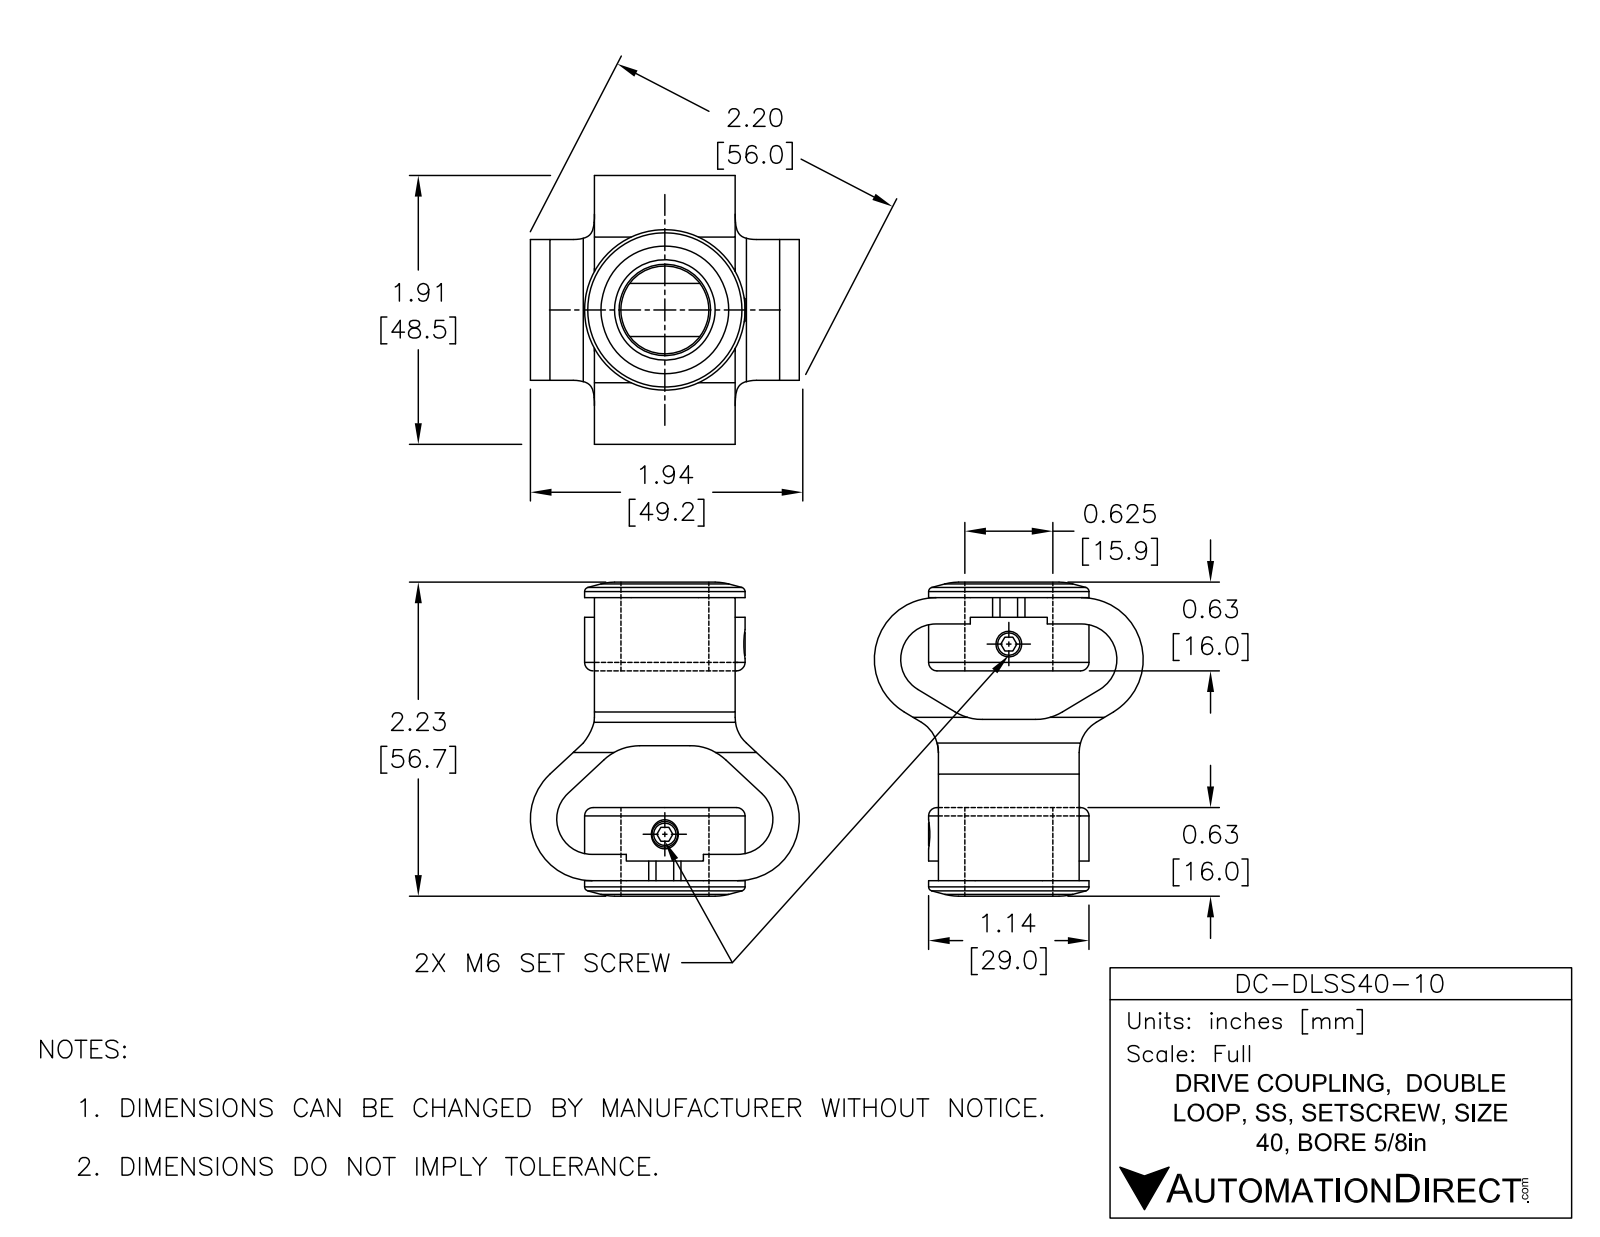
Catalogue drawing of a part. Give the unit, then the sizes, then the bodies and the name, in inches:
Units: inches
Overall size (bounding box): 2.231 × 1.91 × 1.91
Round holes (diameter × count): ⌀0.163 ×2, ⌀0.625 ×1
Round bosses / shafts (diameter × count): ⌀1.14 ×1
Partial cylindrical surfaces — rounded edges, fillets, slot ends (radius × count): R0.25 ×8, R0.25 ×4, R0.375 ×4, R0.437 ×3, R0.41 ×1, R0.437 ×1
Main face-to-face distances: 1, 0.187, 0.971, 0.626, 0.345, 0.439, 0.532, 0.865, 0.959, 0.187
Volume: 1.968 in³ · Surface area: 23.36 in²
Bodies: 1 solid, 187 faces (90 planar, 49 cylindrical, 48 other)
Part name (STEP PRODUCT): DC-DLSS40-10
STEP written by: SolidWorks 2015 (AUTOMOTIVE_DESIGN)
